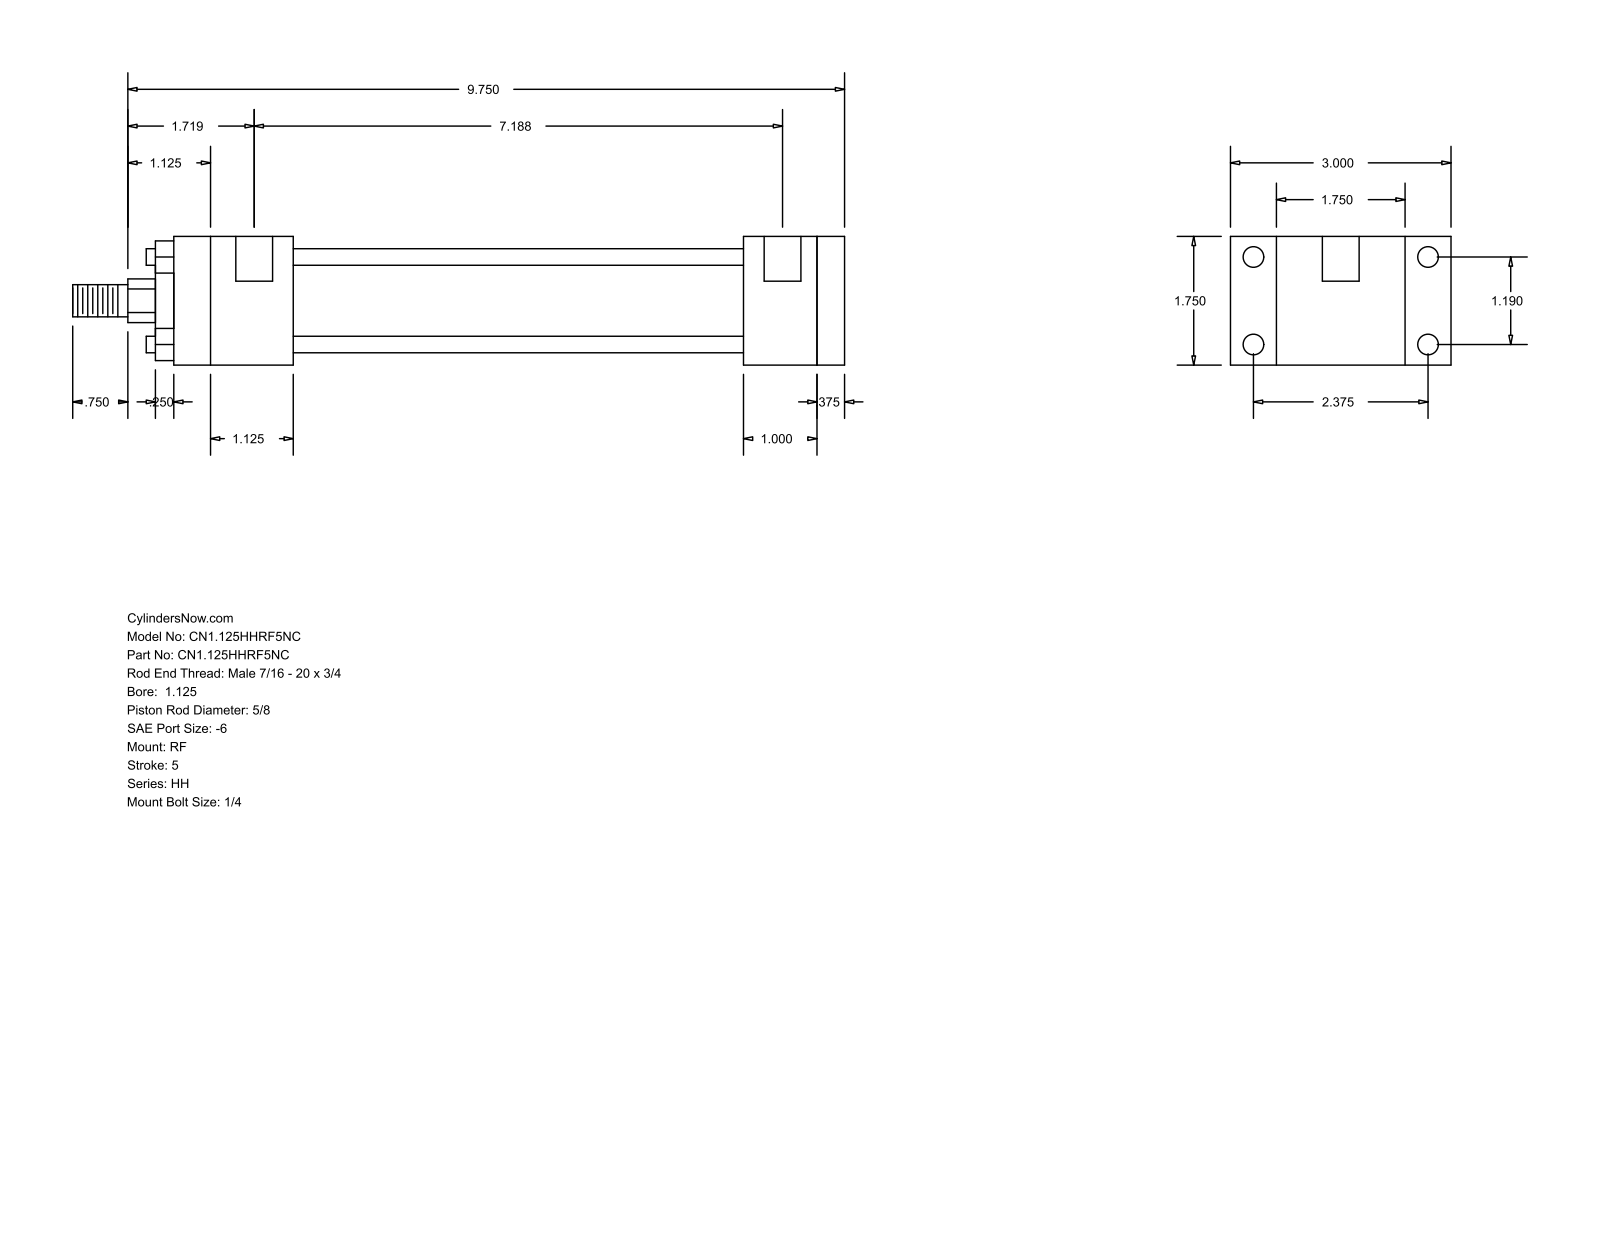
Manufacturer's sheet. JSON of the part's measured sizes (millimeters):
{"part_name": "HH_RF__0112_0.625", "step_written_by": "GSSL Pune (CONFIG_CONTROL_DESIGN)", "units": "millimeters", "bodies": {"solids": 0, "faces": 92, "planar": 64, "cylindrical": 28, "other": 0}, "overall_size": [266.7, 76.2, 44.45], "round_holes": [[5.56, 4], [7.14, 4], [12.7, 2]], "round_bosses_or_shafts": [[5.71, 4], [34.92, 1], [28.57, 1], [15.88, 1], [11.11, 1]], "partial_cylinders_radius": [[7.54, 1]], "face_to_face_distances": [44.46, 9.53, 231.77, 25.4, 34.93, 15.87, 180.97, 190.5, 155.57, 41.27], "hole_center_spacings": [30.22, 60.32, 67.47, 179.39, 3.17, 182.56]}
